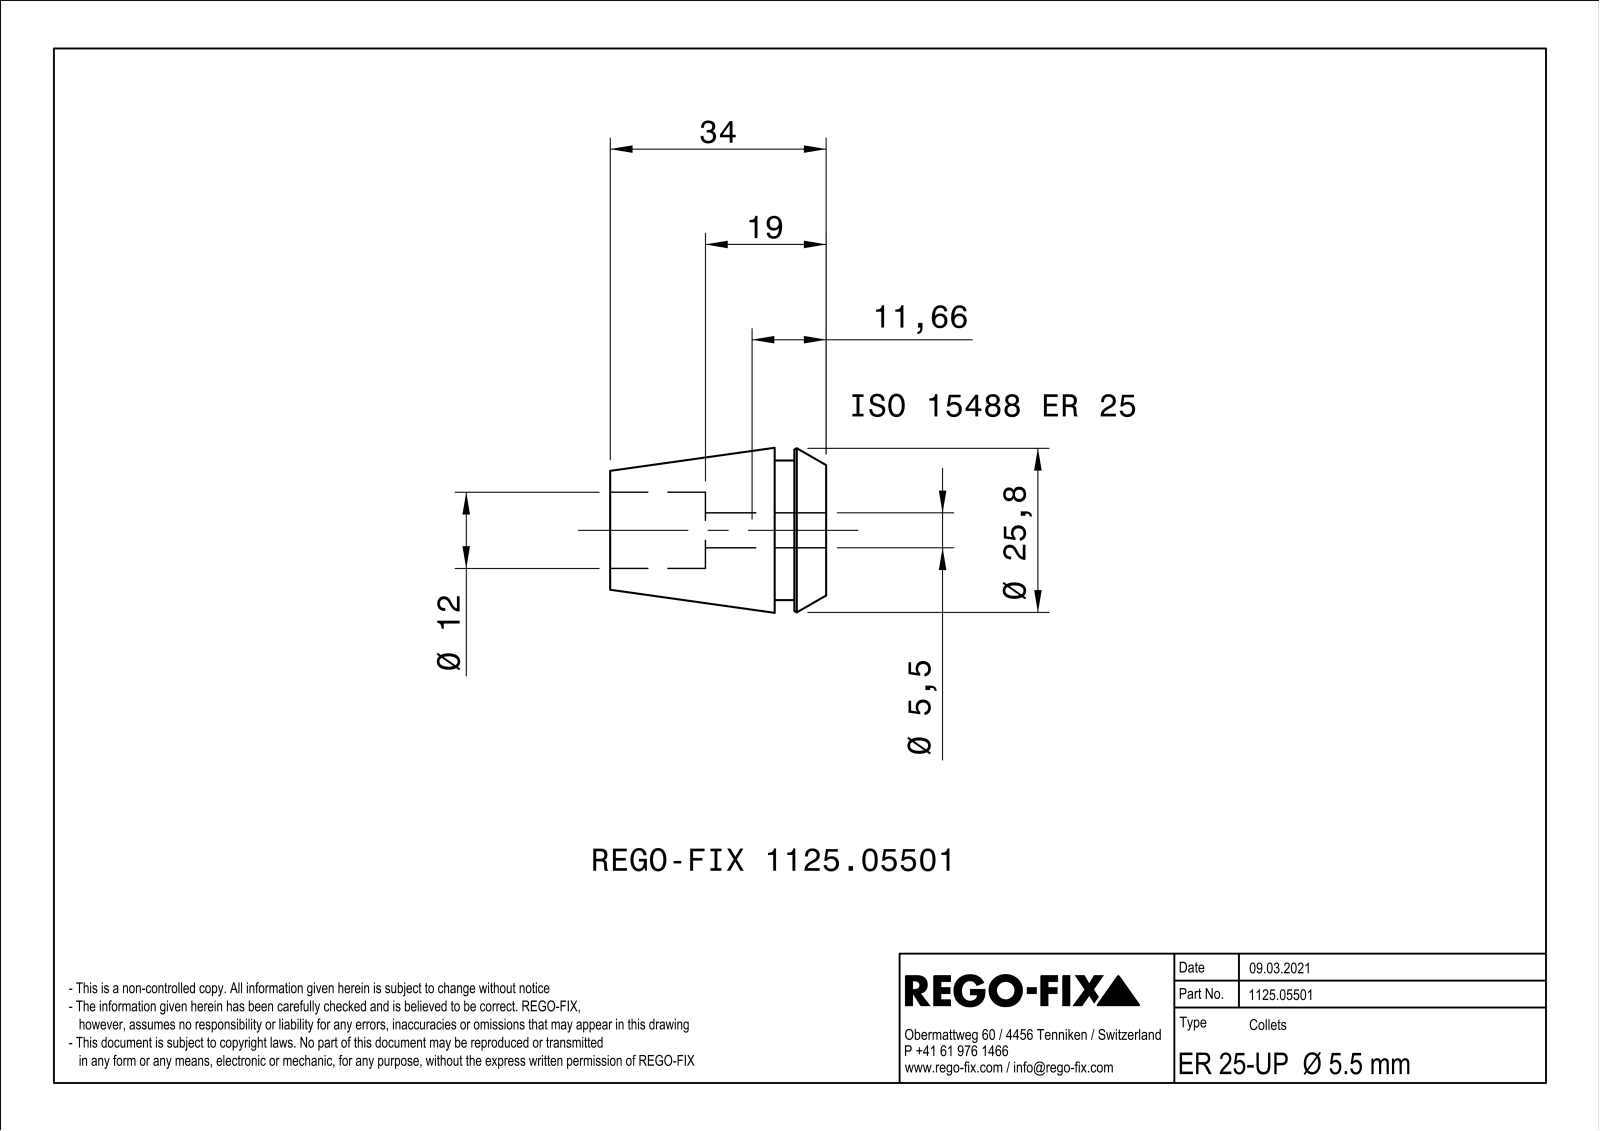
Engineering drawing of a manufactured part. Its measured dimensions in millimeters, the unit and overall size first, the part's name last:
Units: millimetres
Overall size (bounding box): 34 × 25.99 × 25.99
Round holes (diameter × count): ⌀12 ×1
Round bosses / shafts (diameter × count): ⌀22 ×1
Partial cylindrical surfaces — rounded edges, fillets, slot ends (radius × count): R0.4 ×12, R2.75 ×1
Main face-to-face distances: 0.8, 0.82, 0.78, 8.1, 34, 25.9, 5, 3.1, 29, 19
Volume: 9 227 mm³ · Surface area: 9 002 mm²
Bodies: 1 solid, 256 faces (88 planar, 48 cylindrical, 120 other)
Part name (STEP PRODUCT): NOCUT
STEP written by: SIEMENS PLM Software Solid Edge ST10 (AUTOMOTIVE_DESIGN)
